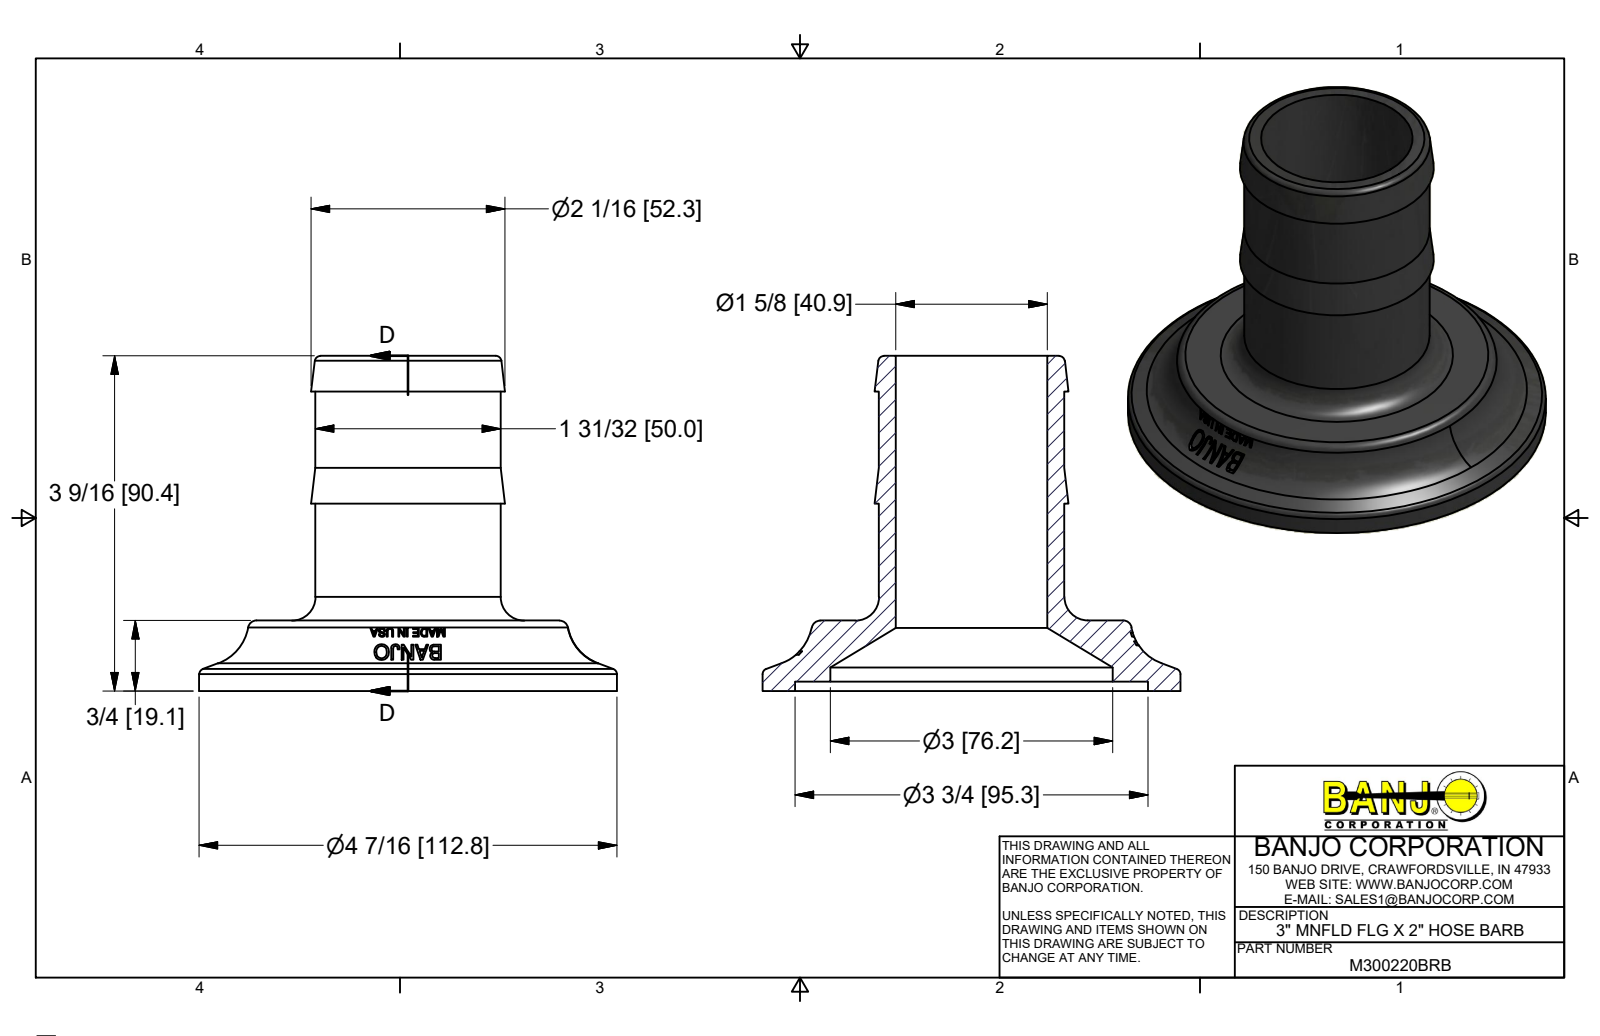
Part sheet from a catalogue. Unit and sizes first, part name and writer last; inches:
Units: inches
Overall size (bounding box): 4.44 × 4.44 × 3.56
Round holes (diameter × count): ⌀1.61 ×1, ⌀3 ×1, ⌀3.75 ×1
Round bosses / shafts (diameter × count): ⌀4.44 ×1, ⌀1.97 ×1
Main face-to-face distances: 0.1, 0.75, 0.65, 3.56, 3.46, 2.81, 1.99, 3.18, 1.89, 3.08
Volume: 7.904 in³ · Surface area: 68.42 in²
Bodies: 1 solid, 399 faces (175 planar, 6 cylindrical, 218 other)
Part name (STEP PRODUCT): M300220BRB
STEP written by: Autodesk Inventor 2017 (AUTOMOTIVE_DESIGN)
